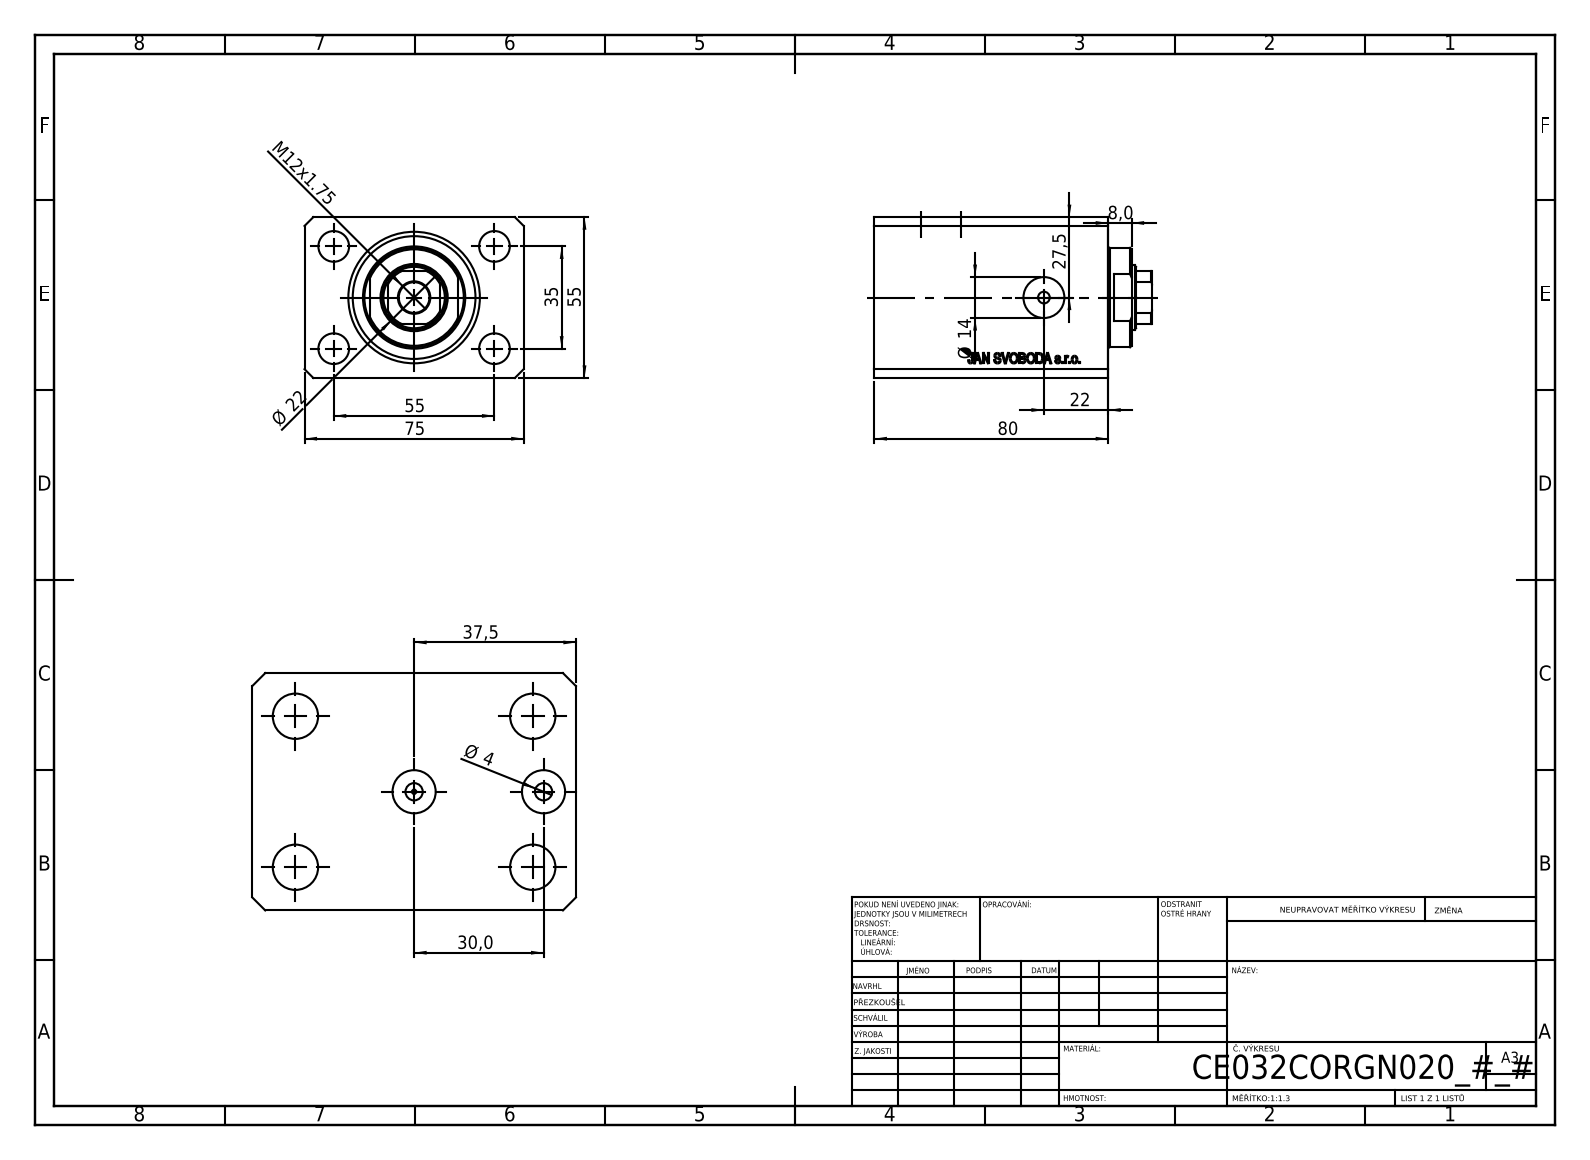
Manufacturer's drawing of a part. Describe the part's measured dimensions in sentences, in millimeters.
The part is named "V250CE_C_VCP; V250CE_VC_C; V250CE_C_Body". Its 3-D file was written by "SolidWorks 2019 (CONFIG_CONTROL_DESIGN)". It is 3 solids with 872 faces: 428 planar, 50 cylindrical and 394 other. Overall it measures 95 by 75 by 55 millimeters. Its volume is 296 169 cubic millimeters and its surface area 64 654 square millimeters. Round holes: 5 of diameter 10.5, 4 of diameter 4, 2 of diameter 10, 2 of diameter 14, 1 of diameter 1.25, 1 of diameter 22, 1 of diameter 32, 1 of diameter 45. Round bosses or shafts: 1 of diameter 34. Partial cylindrical surfaces (rounded edges, fillets, slot ends): 1 of radius 10.5. The main face-to-face distances are 55, 75, 80, 15, 65, 9.9, 55.1, 70.1, 87.66, 8. The hole center spacings are 32.6, 17.68, 35, 55, 60.1, 65.19, 30, 36.
